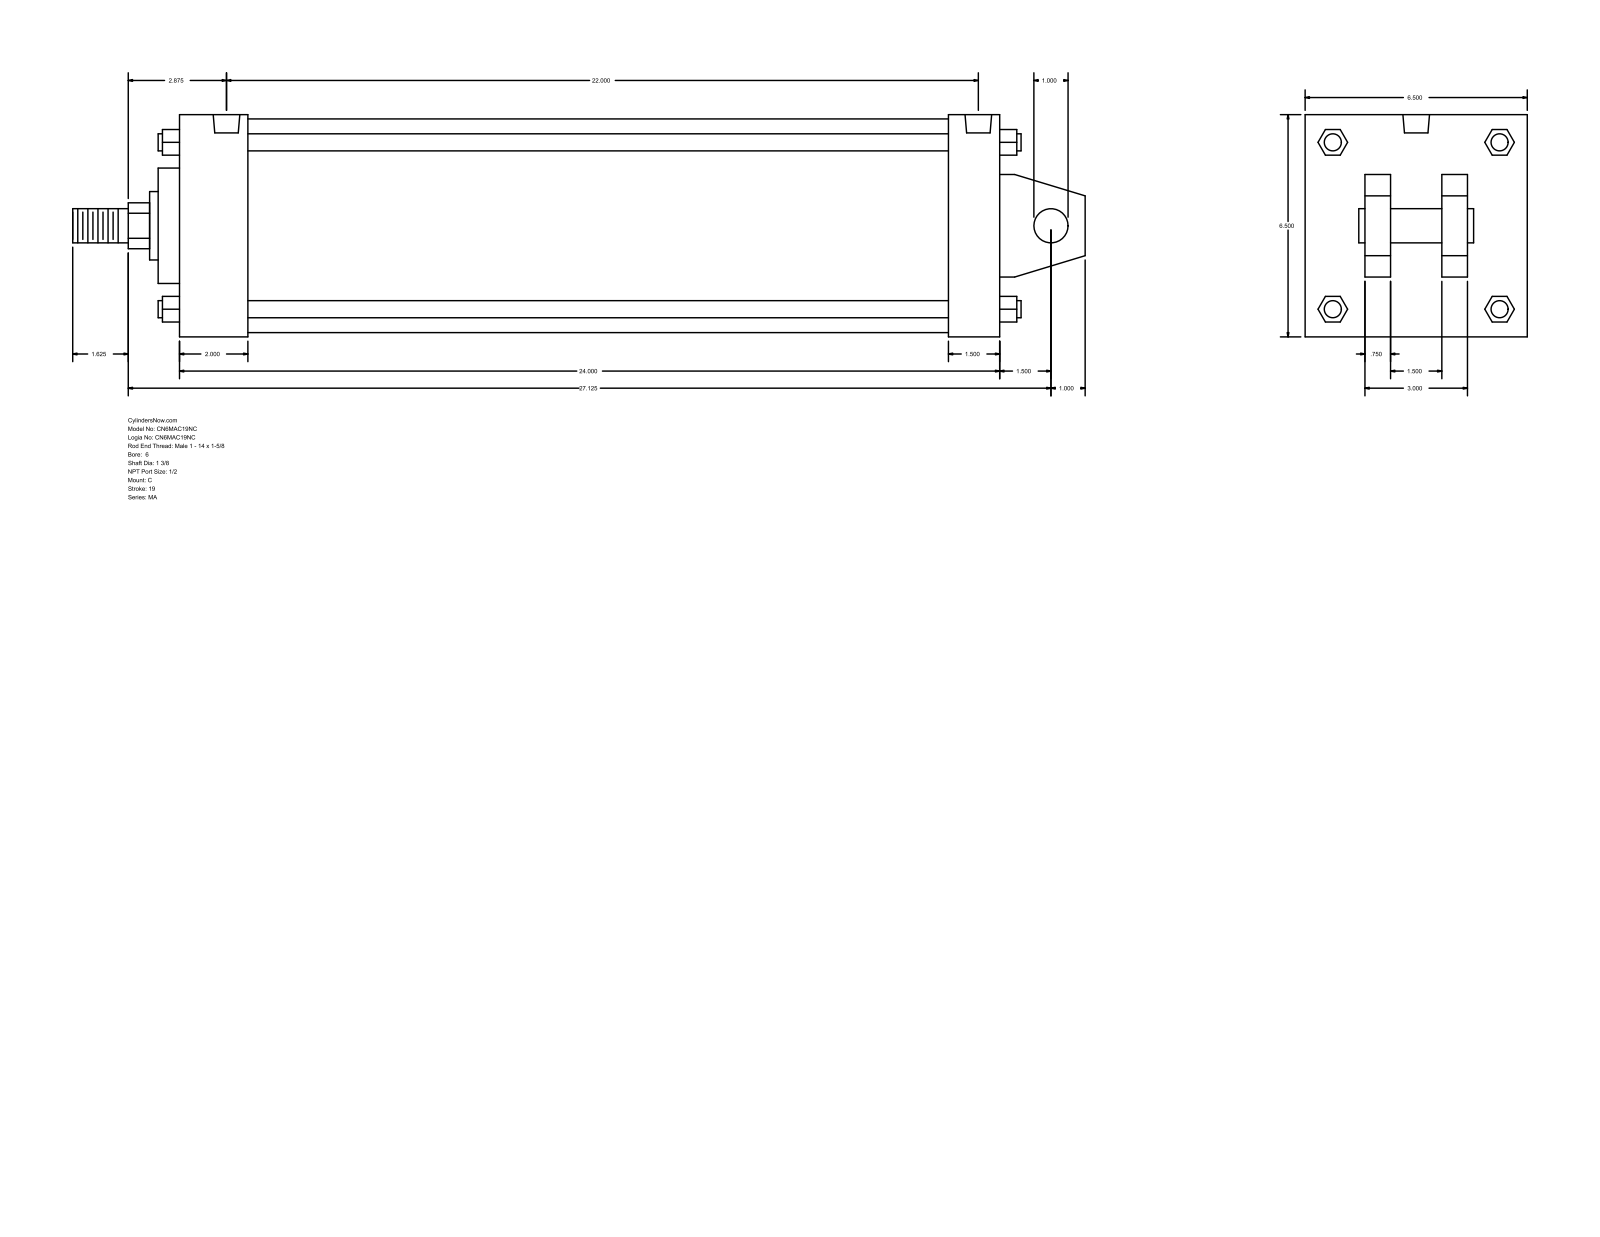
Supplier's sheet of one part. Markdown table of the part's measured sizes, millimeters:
| quantity | value |
| --- | --- |
| part name | MA_C__0600_1.375 |
| STEP written by | GSSL Pune (CONFIG_CONTROL_DESIGN) |
| units | millimeters |
| bodies | 0 solids, 141 faces (109 planar, 32 cylindrical, 0 other) |
| overall size | 752.48 × 165.1 × 165.1 |
| round holes (diameter × count) | 17.46 × 4, 19.77 × 2 |
| round bosses / shafts (diameter × count) | 12.7 × 4, 25.4 × 2, 158.75 × 1, 85.72 × 1, 50.8 × 1, 34.92 × 1 |
| partial cylindrical surfaces (radius × count) | 17.06 × 1 |
| main face-to-face distances | 165.1, 609.6, 38.1, 19.05, 63.5, 101.6, 50.8, 44.45, 120.65, 571.5 |
| hole center spacings | 558.8, 3.18, 555.62, 561.98 |
